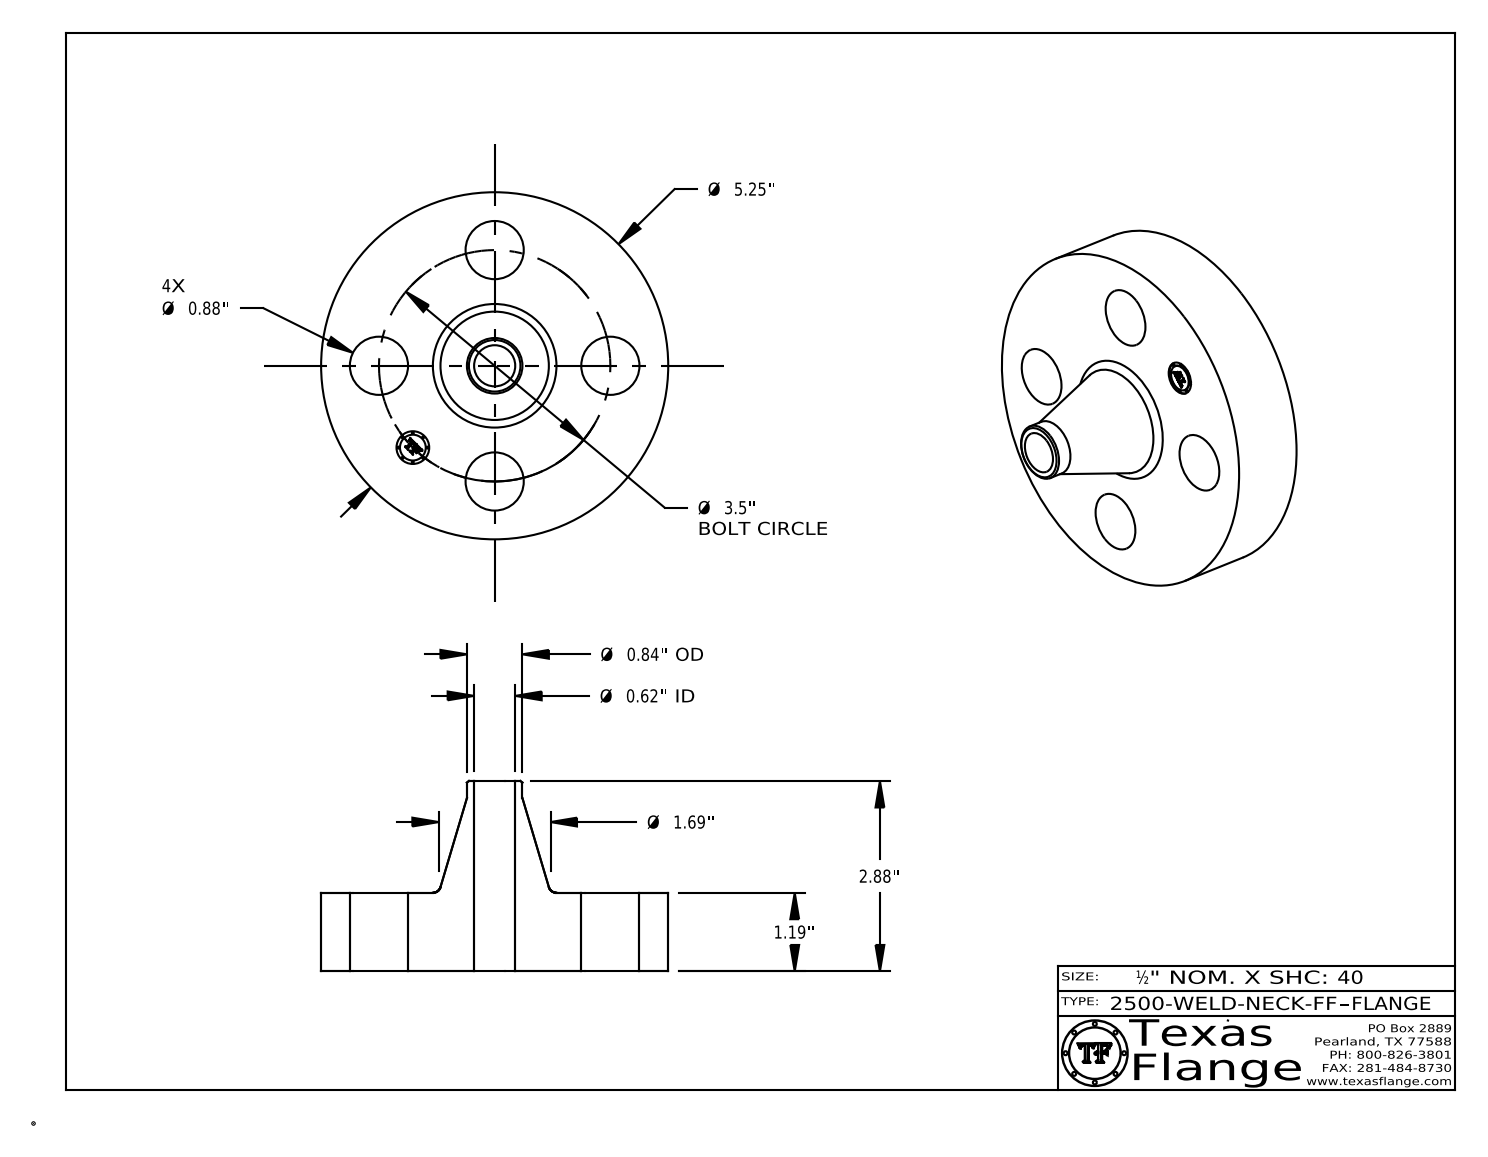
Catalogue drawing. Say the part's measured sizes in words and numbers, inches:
The part is named "2500-WELD-NECK-FF". Its 3-D file was written by "CATIA V5 STEP AP214 (AUTOMOTIVE_DESIGN)". It is 1 solid with 408 faces: 368 planar, 34 cylindrical and 6 other. Overall it measures 5.25 by 5.25 by 2.88 inches. Its volume is 24.01 cubic inches and its surface area 81.08 square inches. Round holes: 4 of diameter 0.88, 1 of diameter 0.495, 1 of diameter 0.622. Round bosses or shafts: 8 of diameter 0.03, 1 of diameter 5.25, 1 of diameter 0.84, 1 of diameter 0.39. The main face-to-face distances are 1.19, 2.88, 1.69, 1.175, 0.015, 1.705, 0.148, 0.145, 0.027, 0.096. The hole center spacings are 1.75, 2.475, 1.339, 3.233, 3.5.
